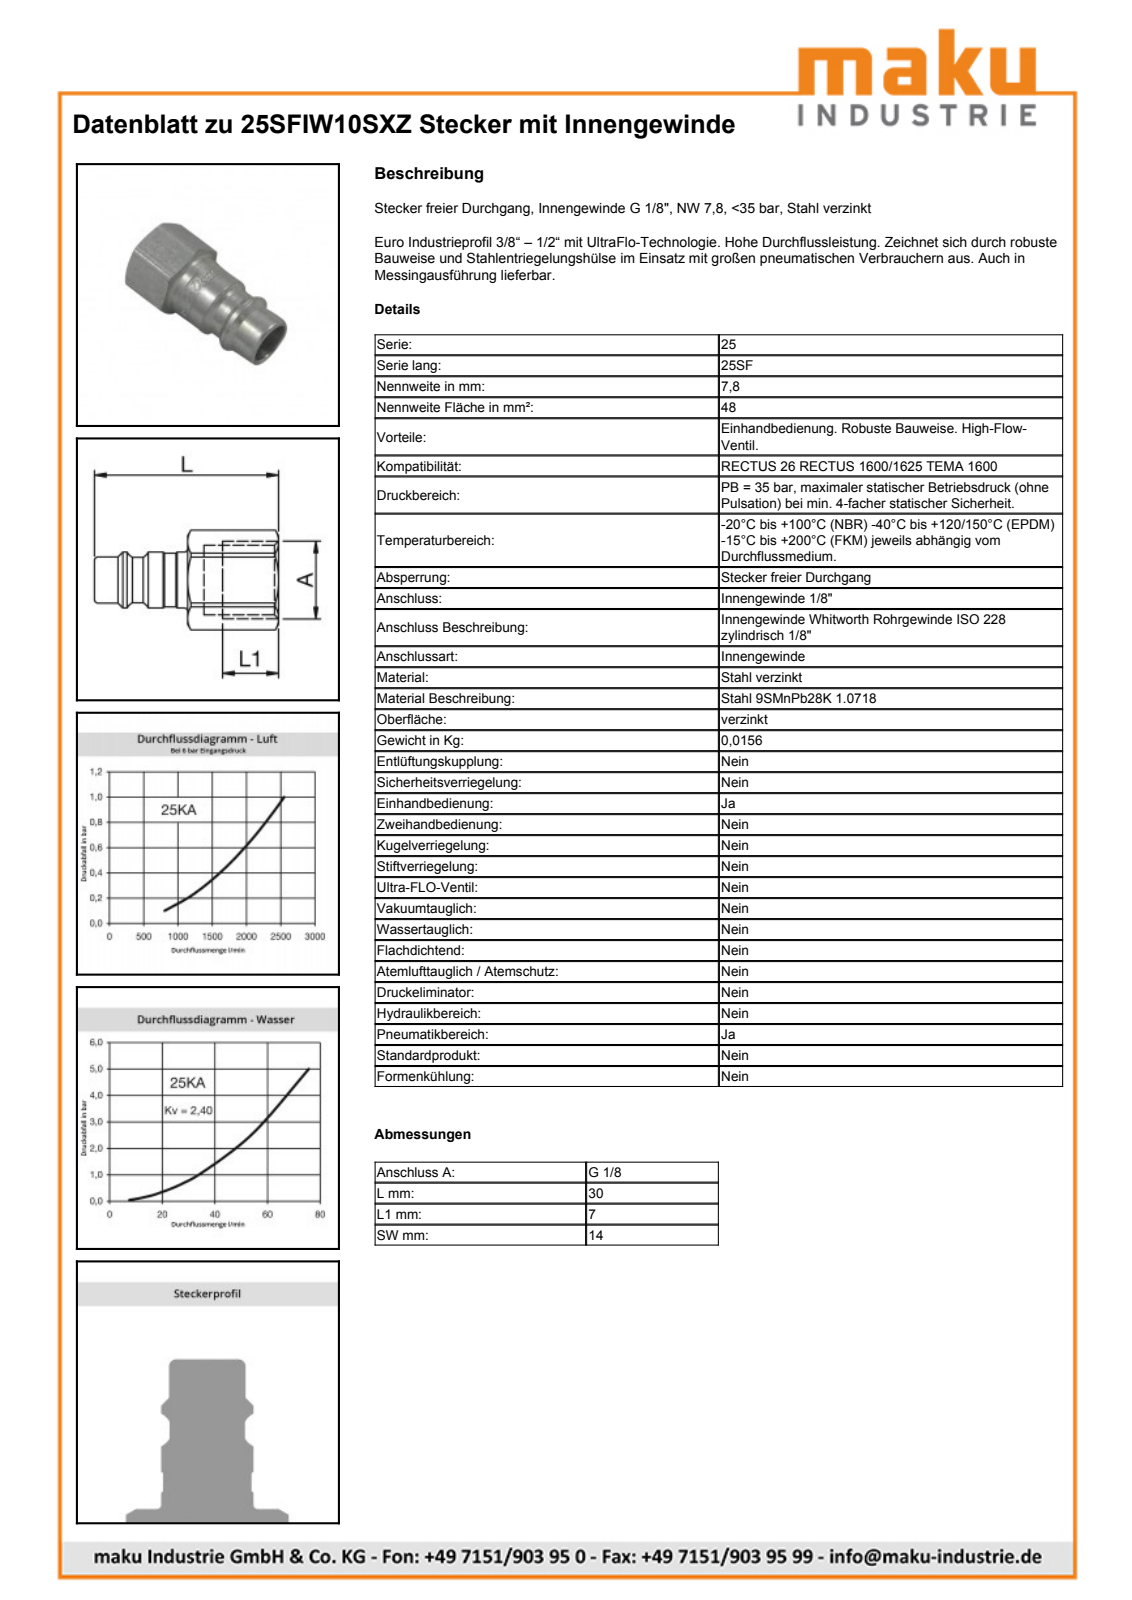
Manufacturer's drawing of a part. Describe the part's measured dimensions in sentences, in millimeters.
The part is named "D103711". Its 3-D file was written by "Autodesk Inventor 2011 (AUTOMOTIVE_DESIGN)". It is 1 solid with 40 faces: 10 planar, 12 cylindrical and 18 other. Overall it measures 30 by 15.8 by 14 millimeters. Its volume is 3 084 cubic millimeters and its surface area 1 695 square millimeters. Round holes: 1 of diameter 9.73. Round bosses or shafts: 1 of diameter 12, 1 of diameter 9.9, 1 of diameter 9.75, 1 of diameter 8.47. Partial cylindrical surfaces (rounded edges, fillets, slot ends): 1 of radius 7.9. The main face-to-face distances are 14, 7, 23, 30, 20, 3, 10.
